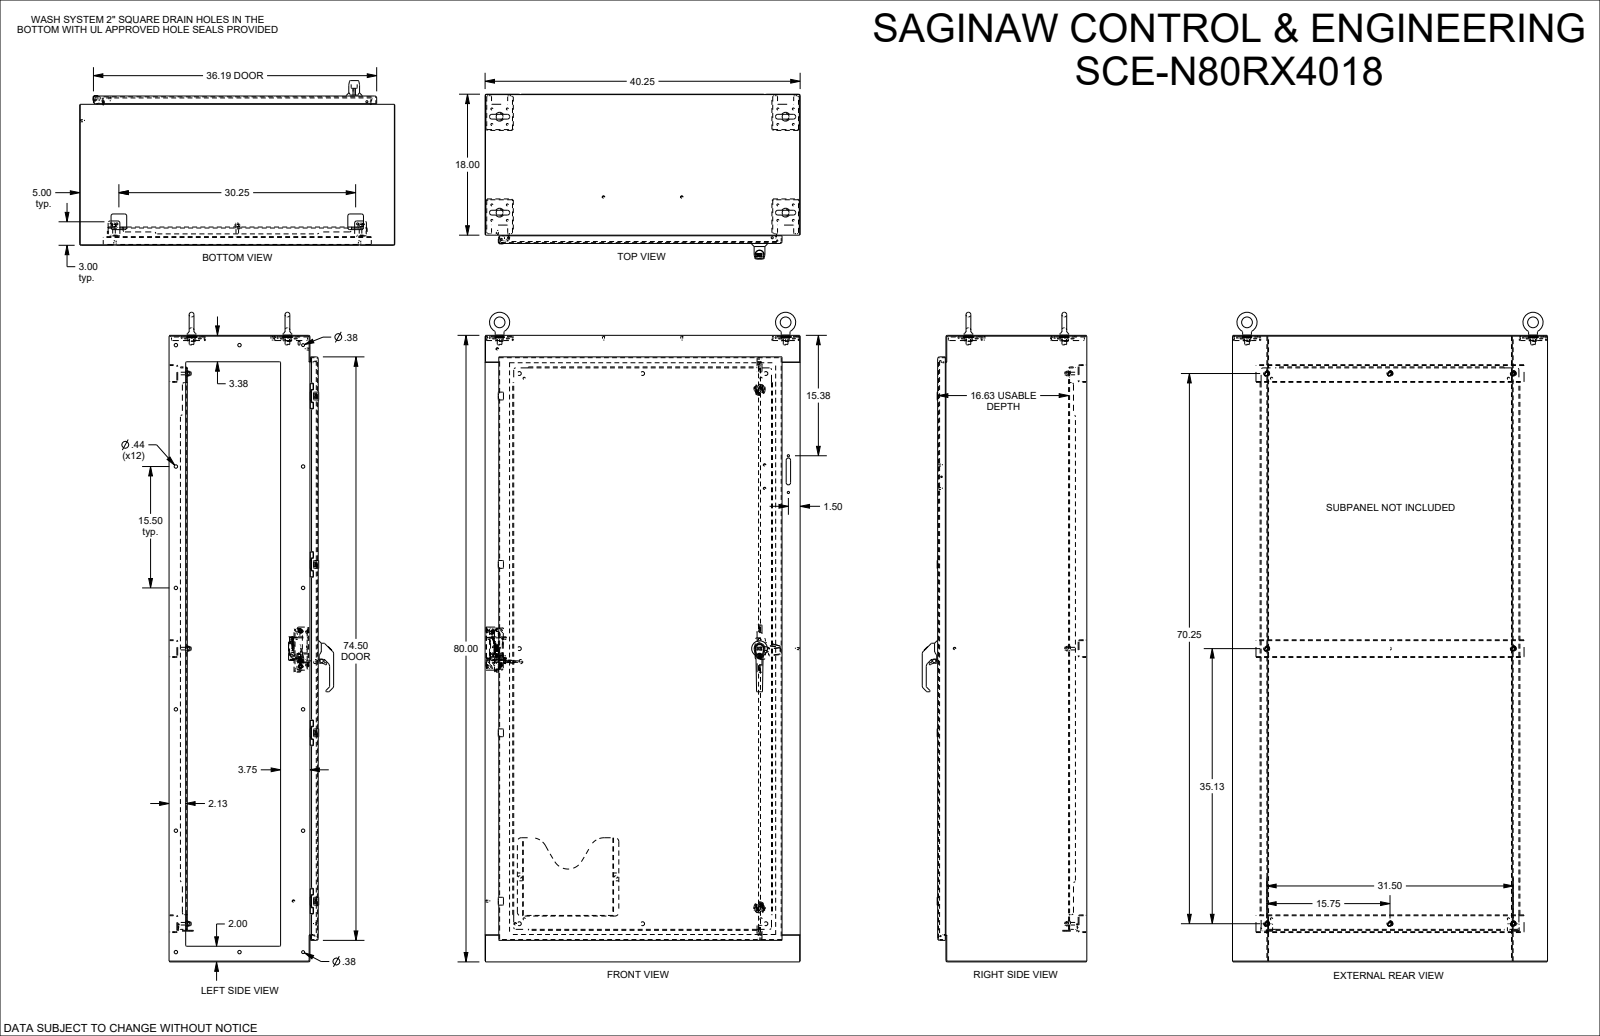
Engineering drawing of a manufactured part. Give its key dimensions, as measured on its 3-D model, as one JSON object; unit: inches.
{"part_name": "SCE-N80RX4018", "step_written_by": "SolidWorks 2023 (AUTOMOTIVE_DESIGN)", "units": "inches", "bodies": {"solids": 27, "faces": 4266, "planar": 1638, "cylindrical": 1524, "other": 1104}, "overall_size": [80, 40.25, 21.046], "volume_in3": 1188, "surface_area_in2": 22617, "round_holes": [[0.25, 18], [0.375, 10], [0.437, 10], [0.205, 8], [0.244, 8], [0.04, 4], [0.115, 4], [0.17, 4], [0.218, 4], [0.256, 4], [0.875, 4], [0.2, 3]], "round_bosses_or_shafts": [[0.17, 12], [0.25, 10], [0.24, 8], [0.196, 5], [1.4, 2], [0.48, 2], [0.341, 2], [0.3, 2]], "partial_cylinders_radius": [[0.03, 142], [0.015, 110], [0.125, 83], [0.063, 44], [0.167, 38], [0.04, 37], [0.229, 32], [0.25, 26]], "face_to_face_distances": [0.104, 18.954, 18.85, 19.058, 17.896, 1.058, 79.896, 40.146, 17.792, 1.162], "hole_center_spacings": [1.979, 21.5, 15.5, 22.457, 1.4, 31, 35.001, 43]}
